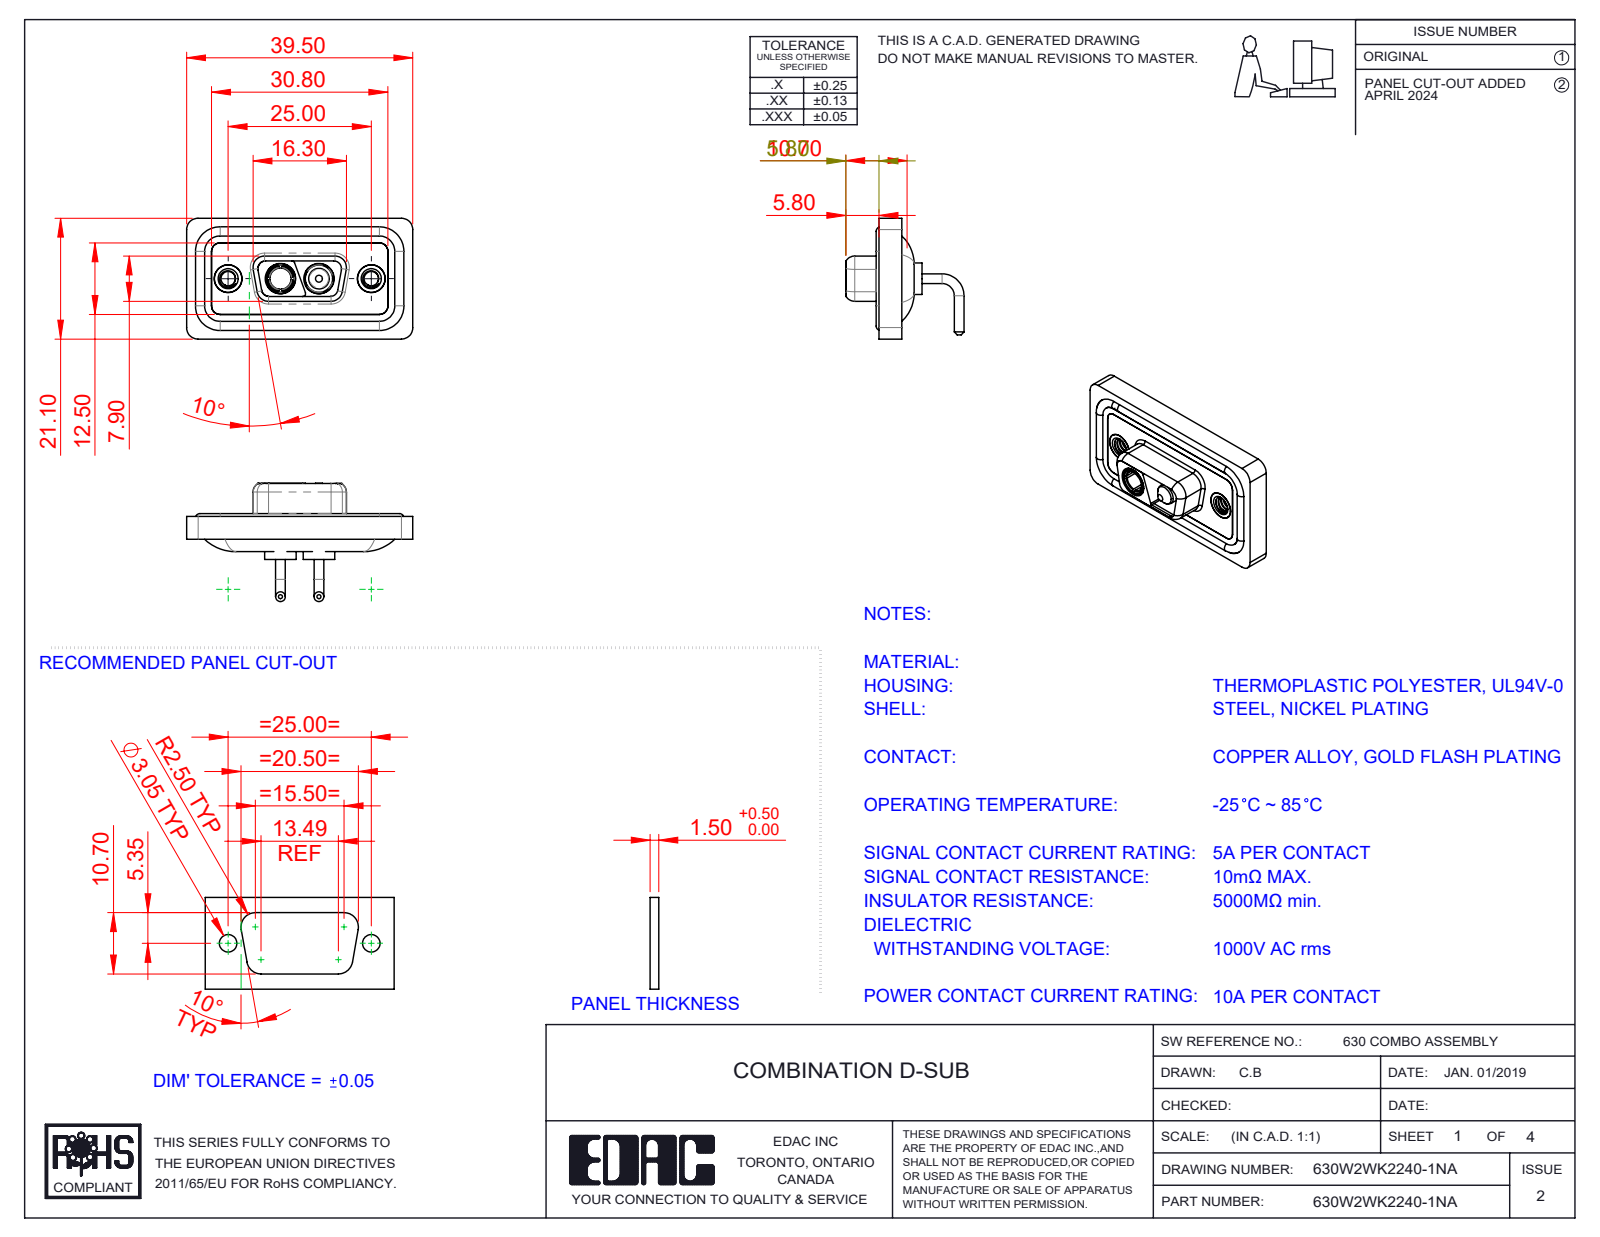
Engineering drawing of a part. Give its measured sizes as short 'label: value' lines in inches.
name: 630Combo Housing_2WK2; 630Combo Shell Rear_09 Contacts; 630Combo Shell Front_09 Contacts; 630Combo Waterproof Housing_09 Contacts (+4 more)
written by: SolidWorks 2023 (CONFIG_CONTROL_DESIGN)
unit: in
bodies: 11 solids, 502 faces (144 planar, 233 cylindrical, 125 other)
size: 1.555 × 0.831 × 0.813
volume: 0.28 in³; area: 11.46 in²
holes: 4× ⌀0.191, 2× ⌀0.098, 2× ⌀0.157, 2× ⌀0.159, 2× ⌀0.197, 2× ⌀0.209, 1× ⌀0.146
bosses: 4× ⌀0.067, 4× ⌀0.063, 2× ⌀0.217, 2× ⌀0.205, 2× ⌀0.195, 2× ⌀0.189, 2× ⌀0.187, 2× ⌀0.148
rounds: 18× R0.059, 18× R0.079, 8× R0.053, 8× R0.063, 6× R0.02, 4× R0.01, 4× R0.024, 4× R0.026
face distances: 0.016, 0.043, 0.114, 0.071, 0.098, 0.063, 0.122, 0.059, 0.083, 0.146
hole spacings: 0.36, 0.624, 0.265, 0.984
